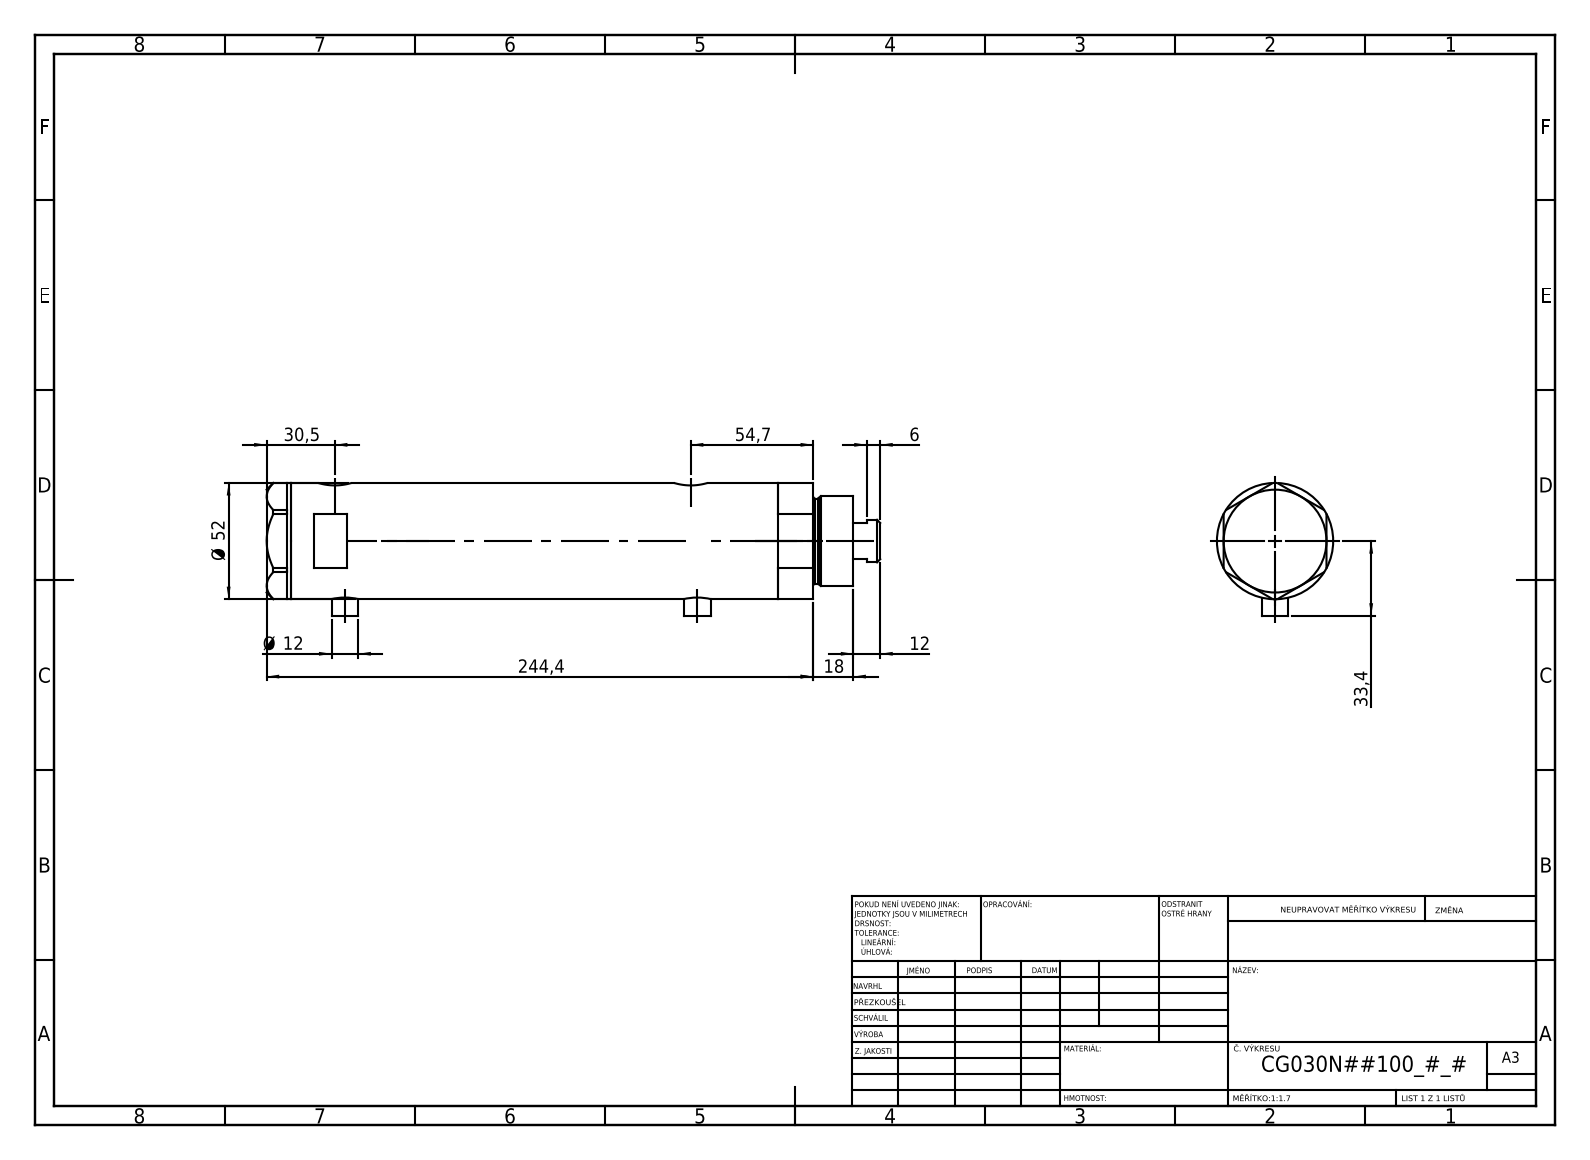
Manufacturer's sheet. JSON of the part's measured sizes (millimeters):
{"part_name": "V270CG_BACK; V270CG_FRONT; V270CG_MIDDLE; V270CG_VC", "step_written_by": "SolidWorks 2019 (CONFIG_CONTROL_DESIGN)", "units": "millimeters", "bodies": {"solids": 4, "faces": 134, "planar": 65, "cylindrical": 49, "other": 20}, "overall_size": [274.4, 59.4, 52], "volume_mm3": 498565, "surface_area_mm2": 106603, "round_holes": [[9.73, 2], [12.5, 2], [15, 2], [6.5, 1], [20, 1], [21.5, 1], [30, 1], [33, 1], [44, 1]], "round_bosses_or_shafts": [[12, 2], [52, 1], [40, 1], [38, 1], [19, 1]], "face_to_face_distances": [181.5, 23.8, 157.7, 11, 34.8, 192.5, 46, 228.9, 217.9, 194.1], "hole_center_spacings": [2.9, 4.5, 154.7, 157.6, 159.2, 162.1]}
